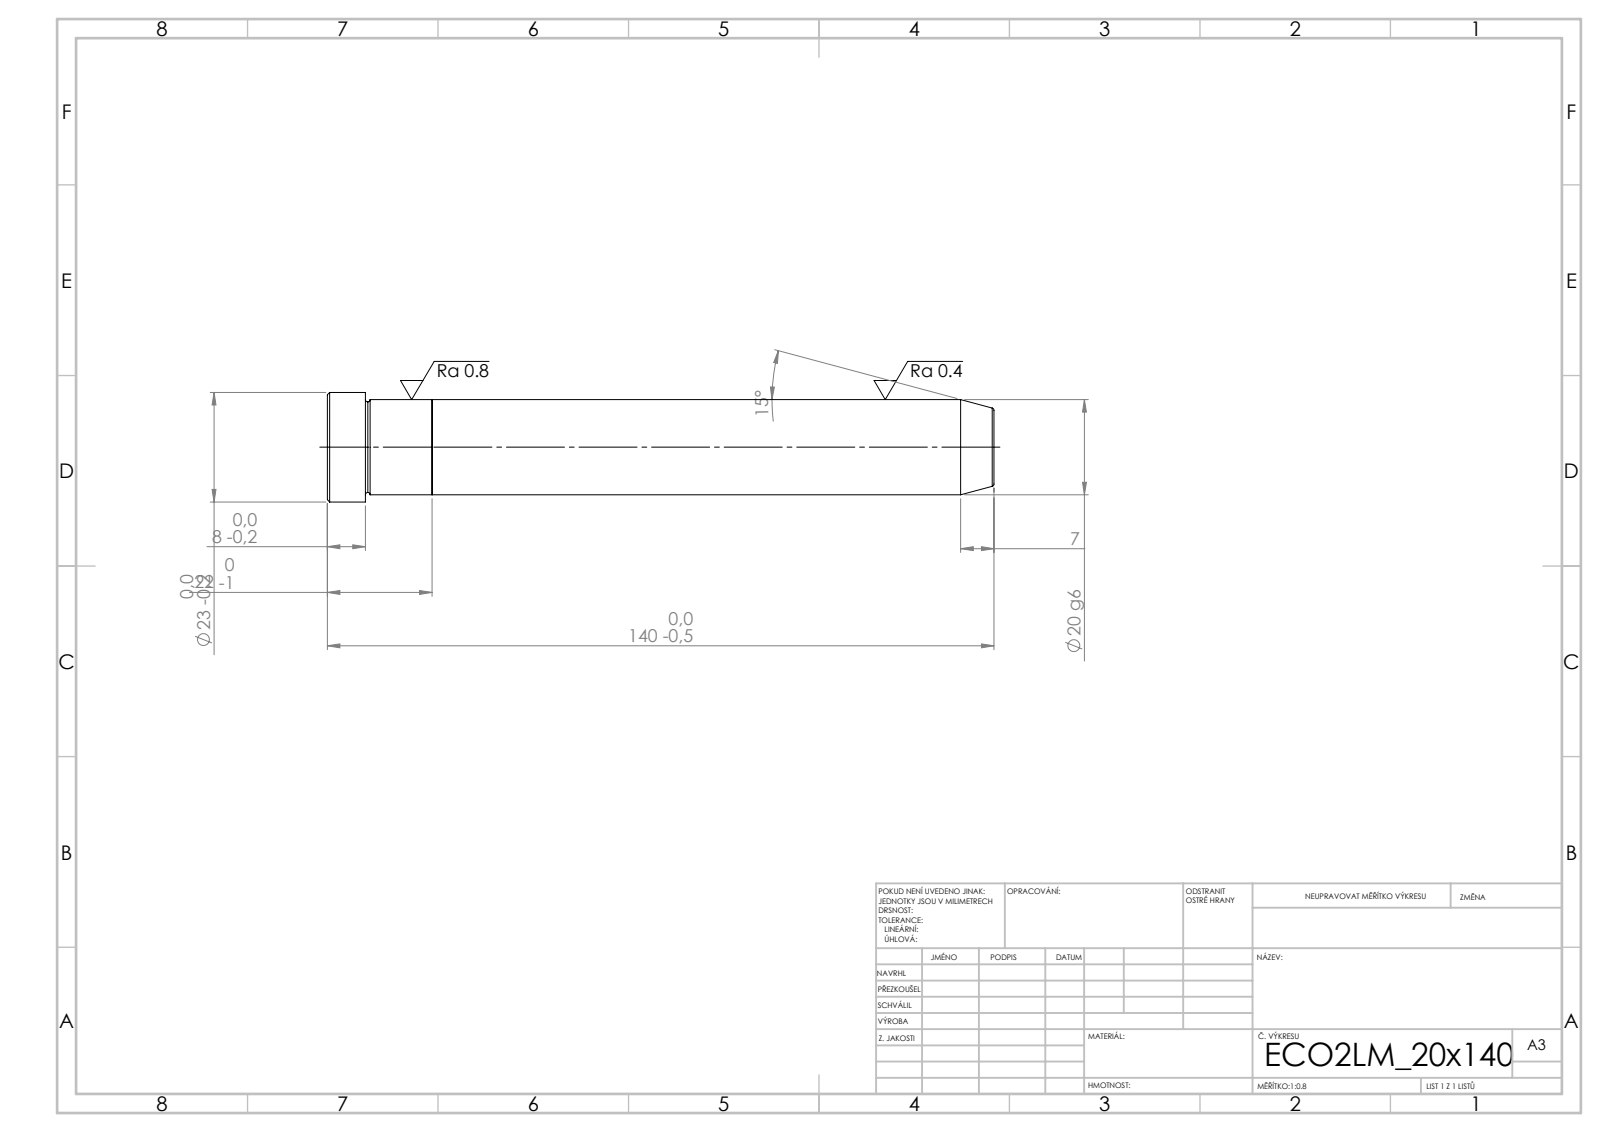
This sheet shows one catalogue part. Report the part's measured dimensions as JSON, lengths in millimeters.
{"step_written_by": "SolidWorks 2019 (CONFIG_CONTROL_DESIGN)", "units": "millimeters", "bodies": {"solids": 2, "faces": 21, "planar": 5, "cylindrical": 6, "other": 10}, "overall_size": [140, 23, 23], "volume_mm3": 44372, "surface_area_mm2": 10203, "round_bosses_or_shafts": [[23, 1], [20, 1]], "face_to_face_distances": [22, 118, 140, 132, 14, 8]}
